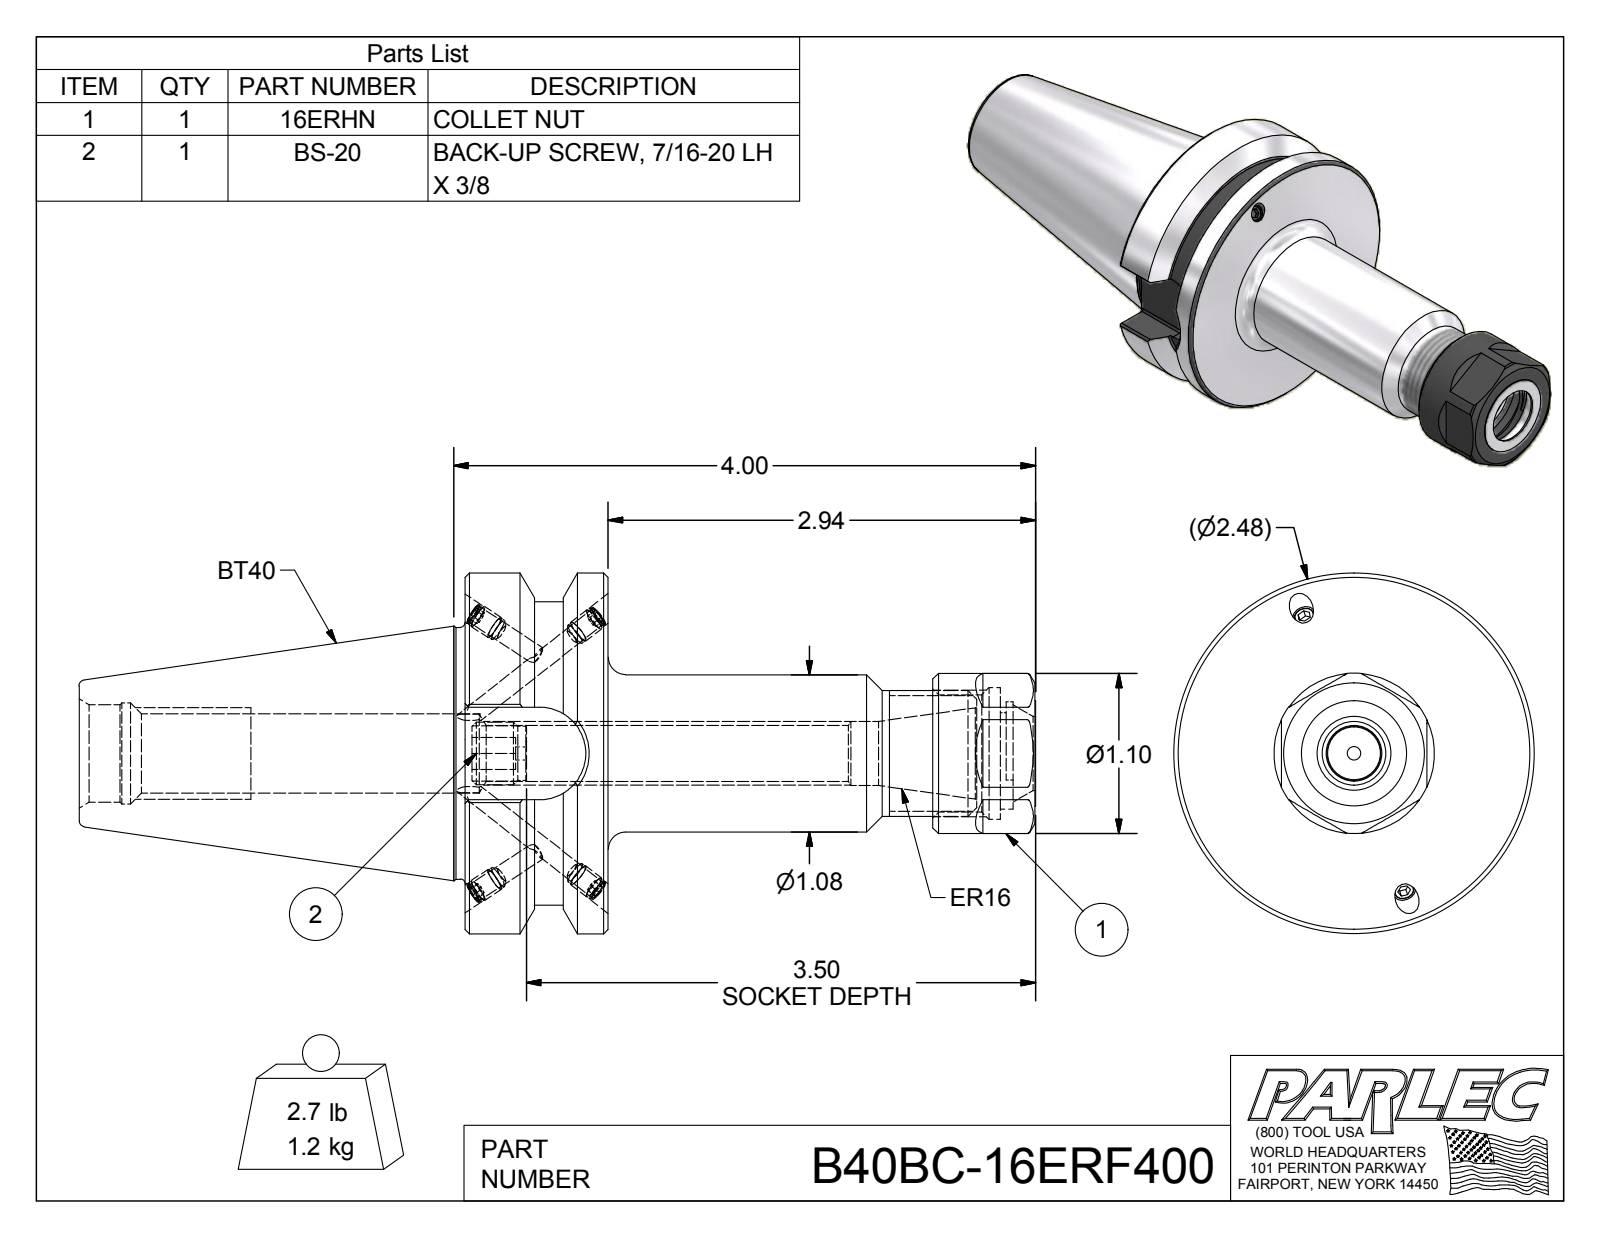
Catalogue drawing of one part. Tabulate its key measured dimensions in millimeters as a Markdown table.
| quantity | value |
| --- | --- |
| part name | B40BCB-16ER4-1; 029-965; 16ERHN; BS-20 (+1 more) |
| STEP written by | Autodesk Inventor 2016 (AUTOMOTIVE_DESIGN) |
| units | millimeters |
| bodies | 7 solids, 201 faces (93 planar, 53 cylindrical, 55 other) |
| overall size | 167 × 62.99 × 62.99 |
| volume | 154 086 mm³ |
| surface area | 34 673 mm² |
| round holes (diameter × count) | 3.3 × 4, 4.1 × 4, 2.29 × 1, 9.73 × 1, 11.18 × 1, 12.4 × 1, 13.84 × 1, 17.01 × 1, 17.02 × 1, 17.62 × 1, 20.5 × 1, 23 × 1 |
| round bosses / shafts (diameter × count) | 4.2 × 4, 4 × 4, 62.99 × 1, 53.01 × 1, 43.94 × 1, 28 × 1, 27.43 × 1, 22 × 1 |
| partial cylindrical surfaces (radius × count) | 0.51 × 8, 7.24 × 1, 8.09 × 1, 9 × 1 |
| main face-to-face distances | 24.99, 99.62, 74.63, 25.14, 45.22, 10.04, 35.18, 93.92, 68.93, 5.7 |
| hole center spacings | 1.52 |
